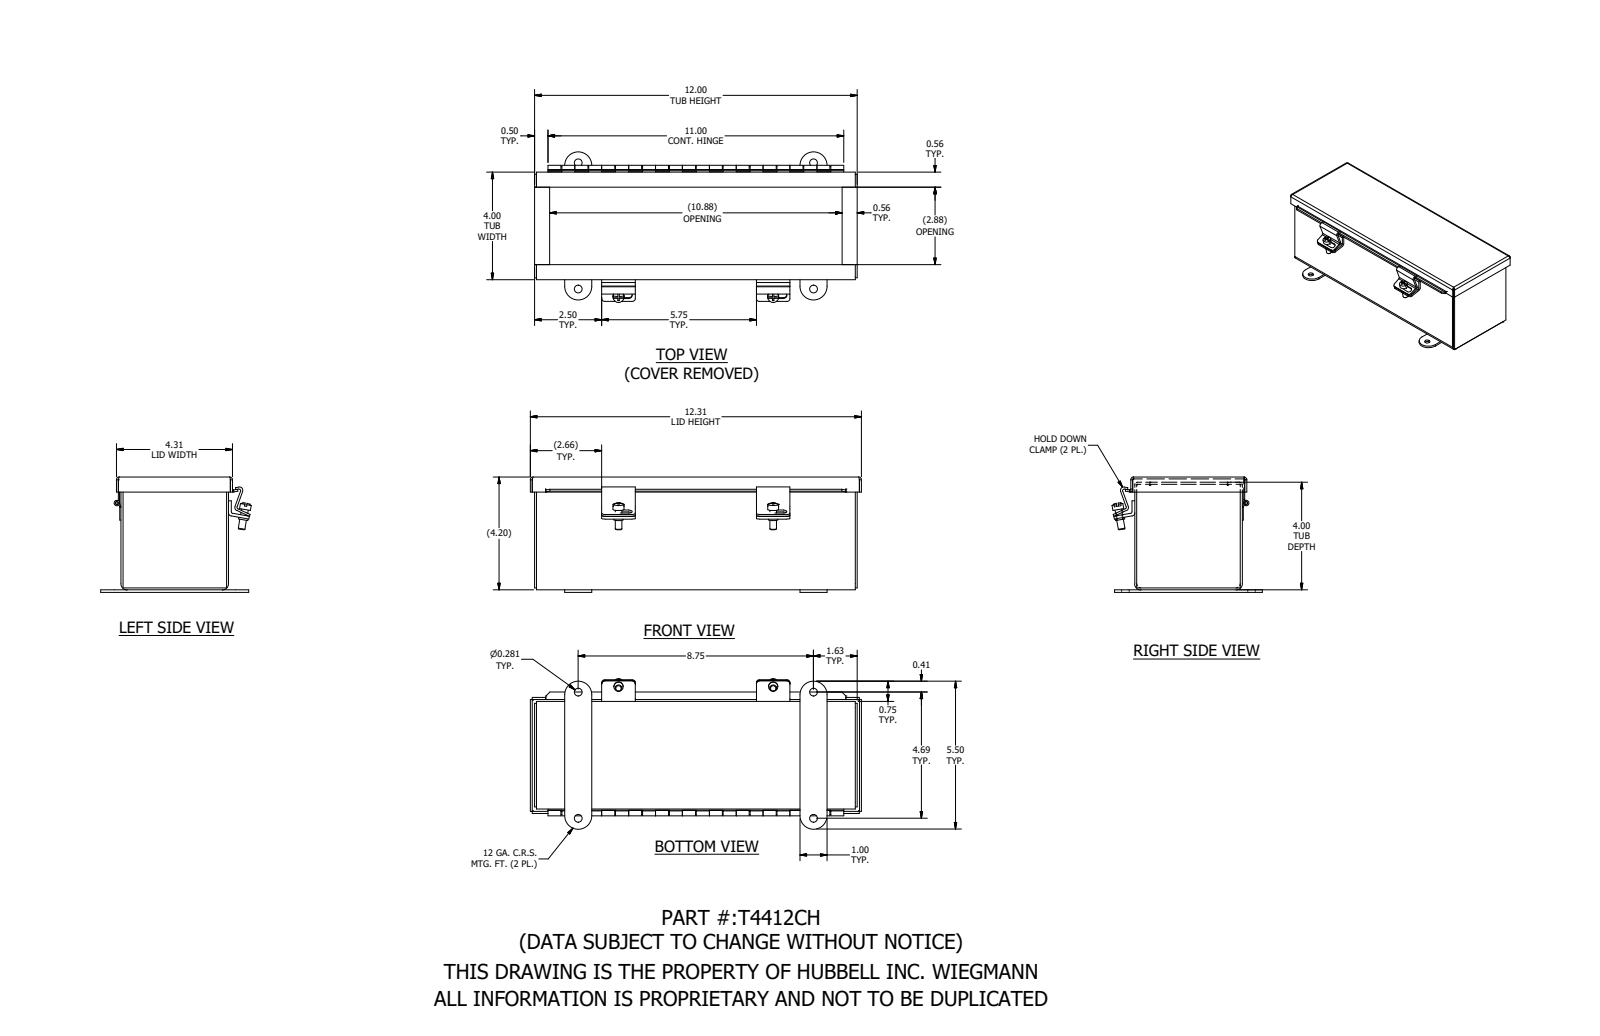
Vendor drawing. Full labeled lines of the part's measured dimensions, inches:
Part name (STEP PRODUCT): T4412CH
STEP written by: SolidWorks 2021 (AUTOMOTIVE_DESIGN)
Units: inches
Bodies: 15 solids, 420 faces (234 planar, 168 cylindrical, 18 other)
Overall size (bounding box): 12.313 × 5.595 × 4.293
Volume: 21.23 in³ · Surface area: 598.7 in²
Round holes (diameter × count): ⌀0.281 ×4, ⌀0.196 ×2, ⌀0.116 ×1
Round bosses / shafts (diameter × count): ⌀0.41 ×2, ⌀0.344 ×2, ⌀0.25 ×2, ⌀0.2 ×1, ⌀0.1 ×1
Partial cylindrical surfaces — rounded edges, fillets, slot ends (radius × count): R0.031 ×9, R0.105 ×9, R0.125 ×8, R0.133 ×4, R0.5 ×4, R0.063 ×3, R0.126 ×3, R0.156 ×2
Main face-to-face distances: 0.074, 3.926, 4.125, 4, 3.852, 4.199, 4.051, 4.094, 0.168, 11.926
Hole centre spacings: 4.687, 8.75, 9.926, 5.75
